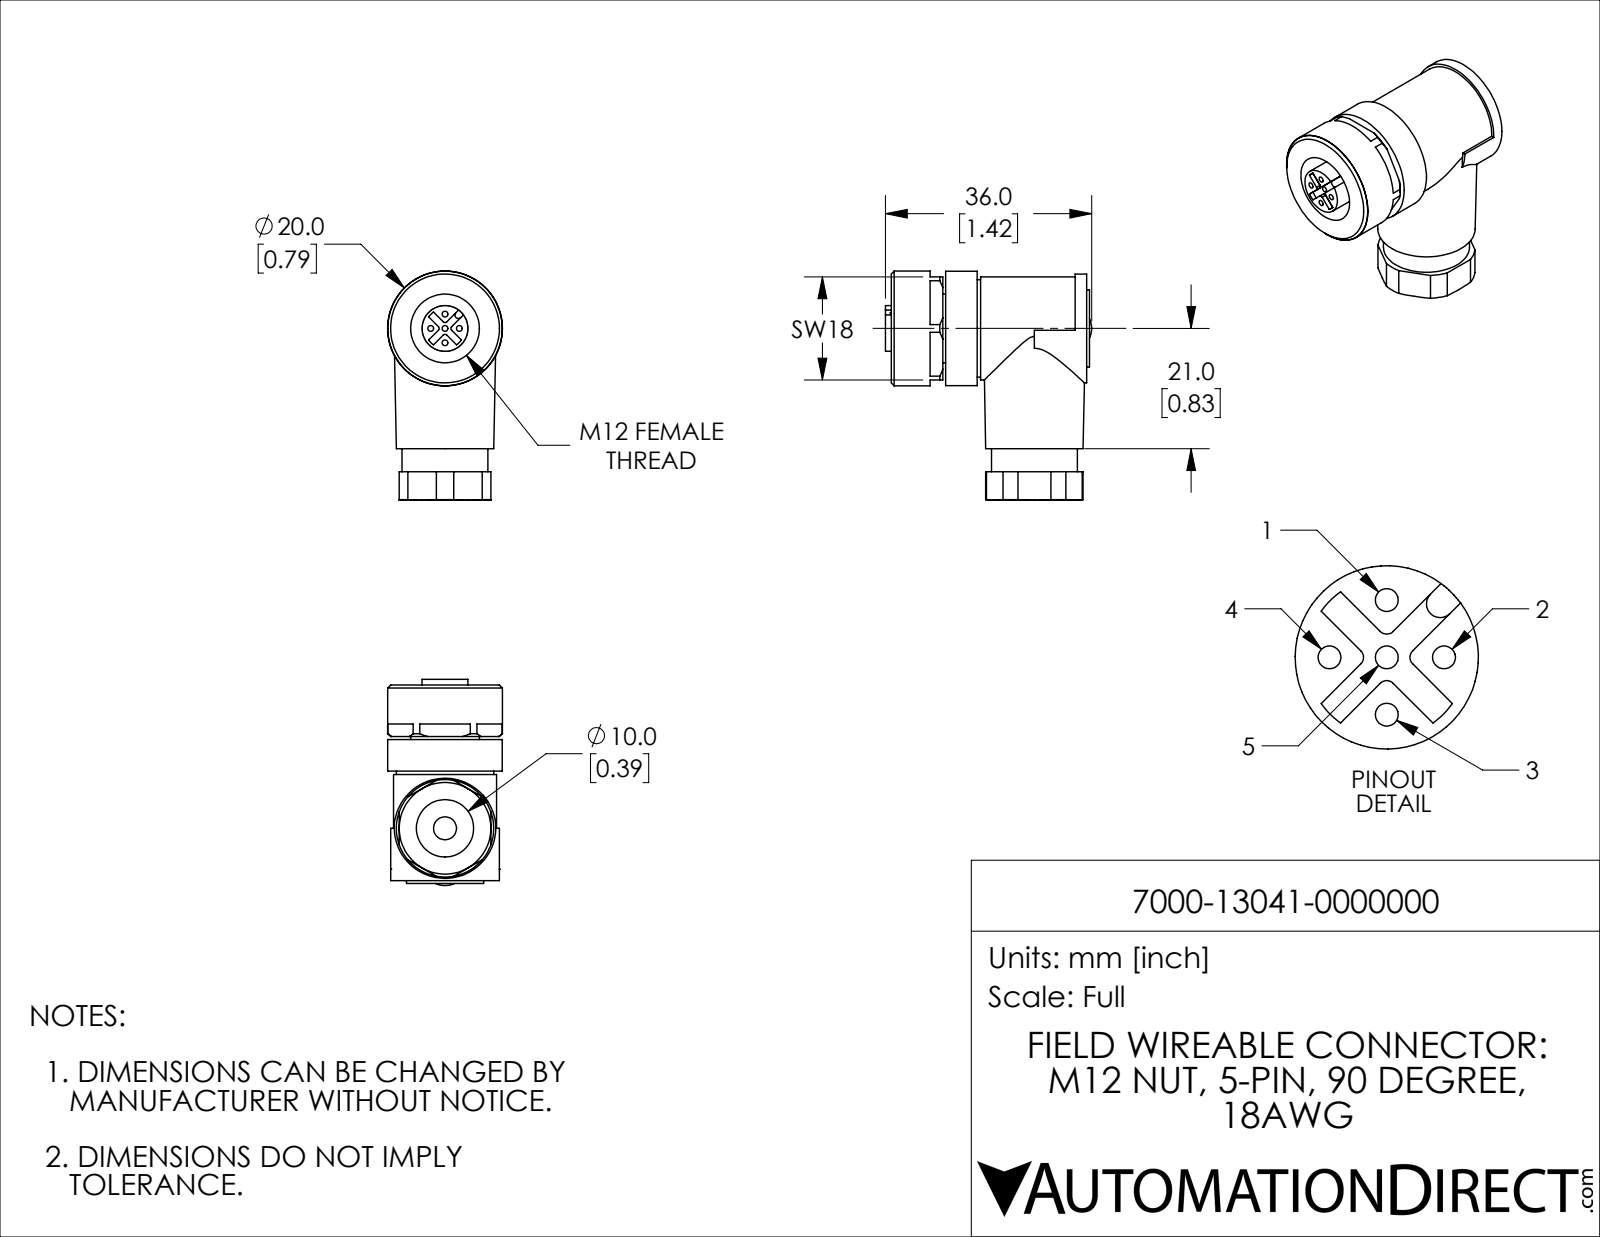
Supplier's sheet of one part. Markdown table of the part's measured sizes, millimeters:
| quantity | value |
| --- | --- |
| part name | 7000-13041-0000000 |
| STEP written by | SolidWorks 2019 (CONFIG_CONTROL_DESIGN) |
| units | millimeters |
| bodies | 1 solid, 125 faces (54 planar, 52 cylindrical, 19 other) |
| overall size | 40 × 36 × 20 |
| volume | 13 000 mm³ |
| surface area | 5 546 mm² |
| round holes (diameter × count) | 1 × 5, 4 × 1, 10 × 1, 12 × 1, 12.5 × 1 |
| round bosses / shafts (diameter × count) | 20 × 1, 20 × 1, 19 × 1, 18 × 1, 17 × 1, 15 × 1, 13.5 × 1, 8 × 1 |
| partial cylindrical surfaces (radius × count) | 0.4 × 4, 0.6 × 1, 3.5 × 1, 8.5 × 1 |
| main face-to-face distances | 0.5, 9.5, 9, 24.6, 25.1, 34.1, 16, 8.5, 1, 15 |
| hole center spacings | 2.5, 3.5, 5 |
